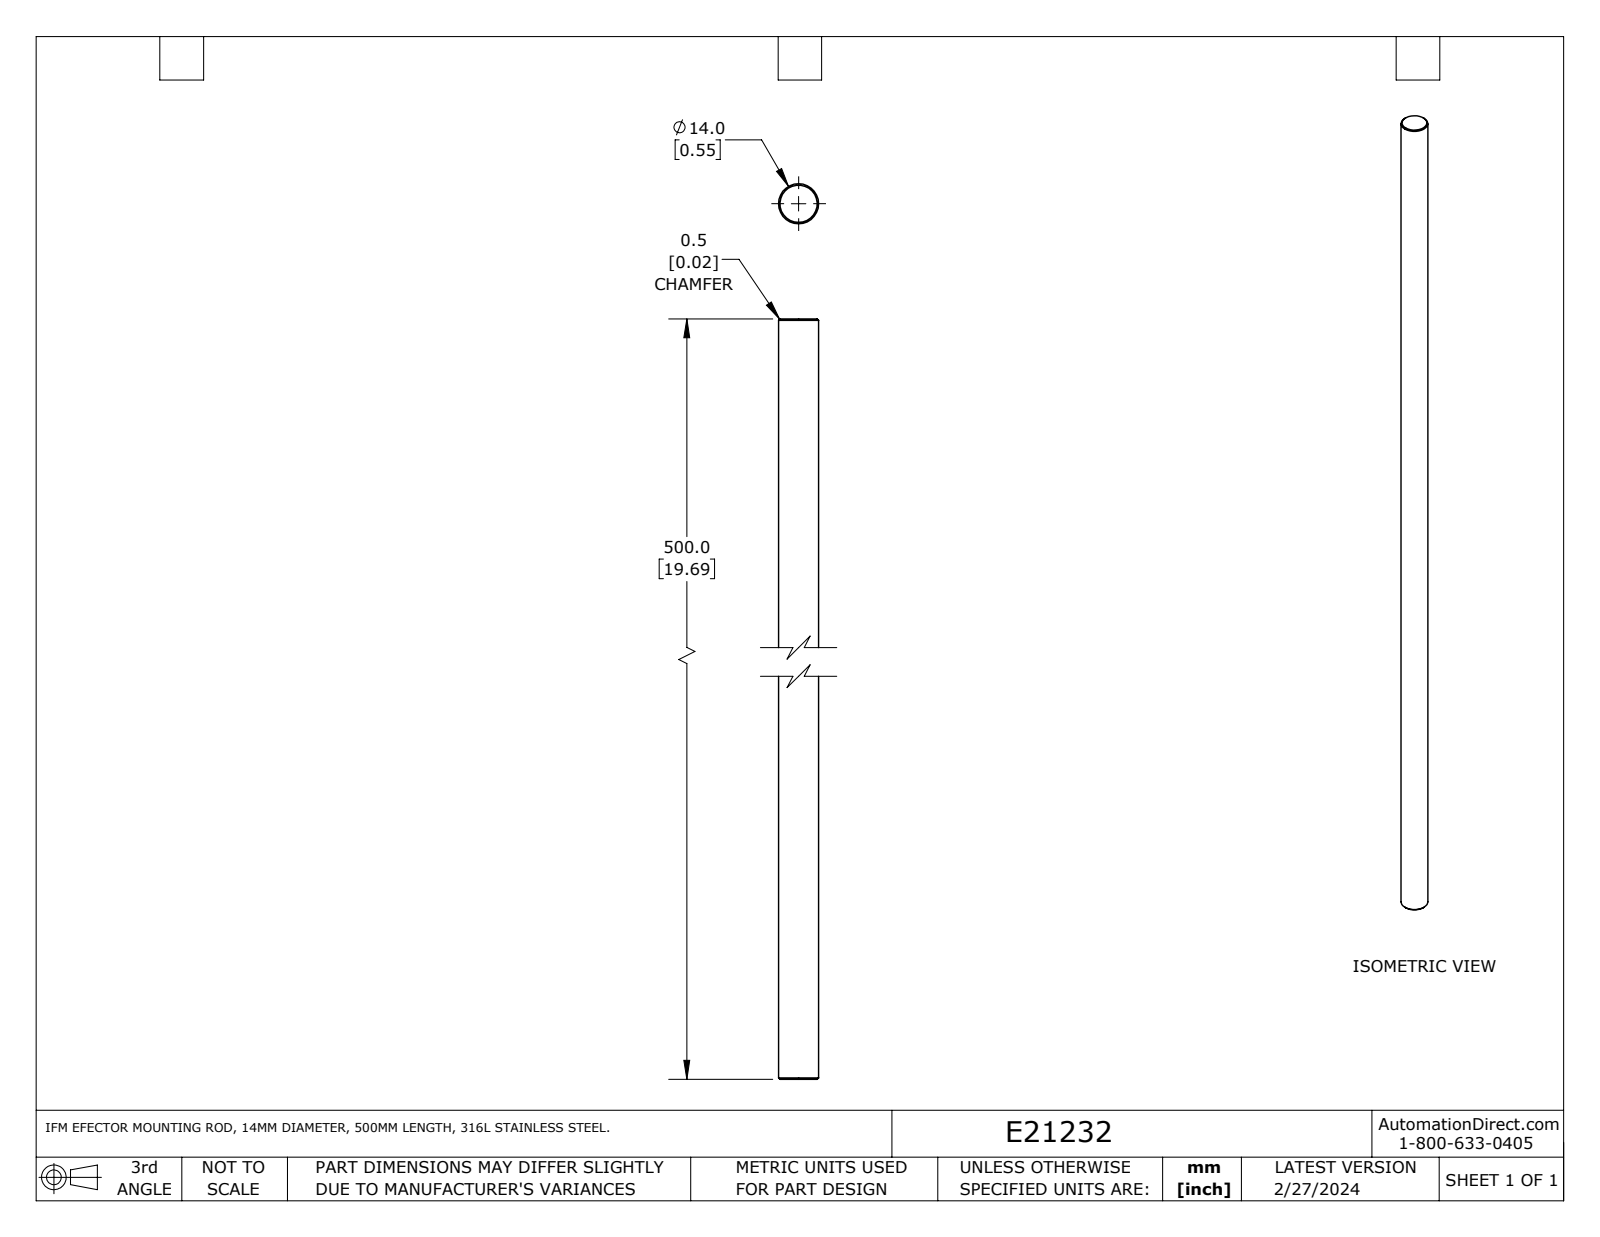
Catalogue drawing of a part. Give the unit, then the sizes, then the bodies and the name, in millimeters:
Units: millimetres
Overall size (bounding box): 500 × 14 × 14
Round bosses / shafts (diameter × count): ⌀14 ×1
Main face-to-face distances: 500
Volume: 76 950 mm³ · Surface area: 22 270 mm²
Bodies: 1 solid, 5 faces (2 planar, 1 cylindrical, 2 other)
Part name (STEP PRODUCT): E21232
STEP written by: SolidWorks 2023 (AUTOMOTIVE_DESIGN)
